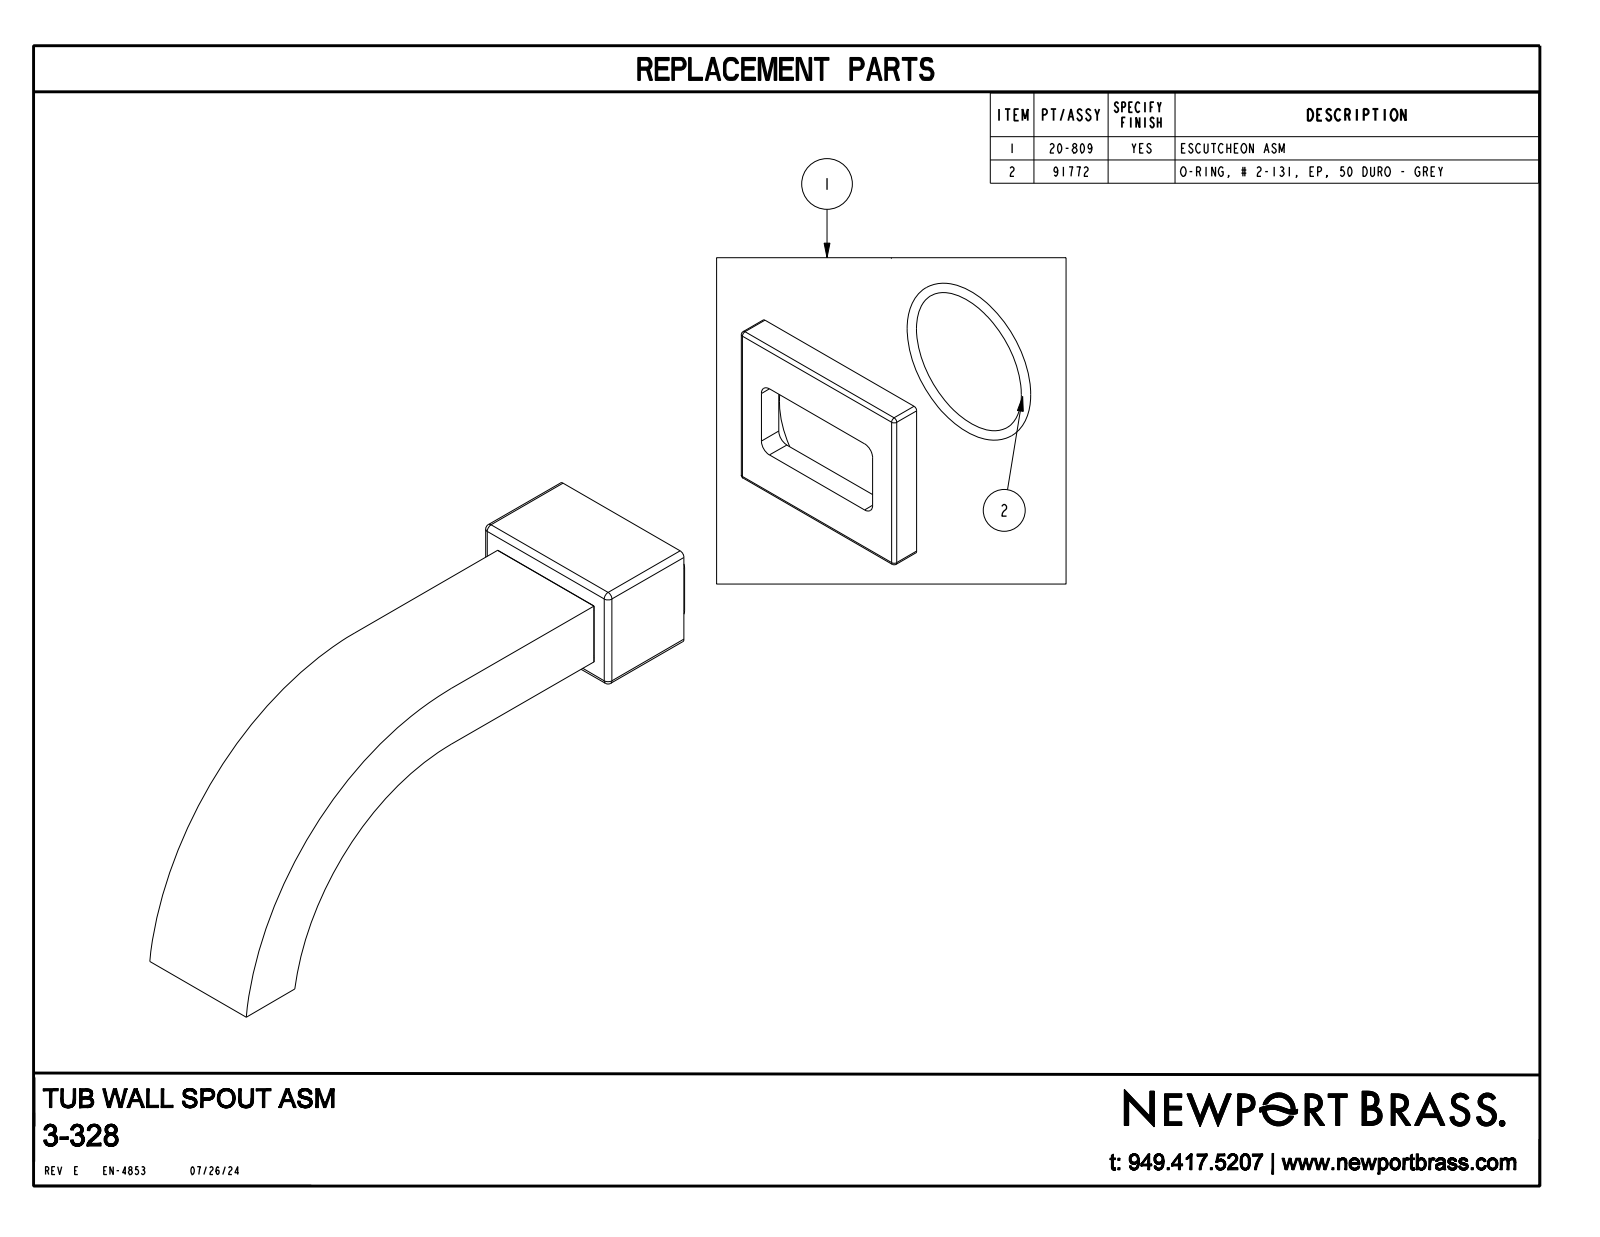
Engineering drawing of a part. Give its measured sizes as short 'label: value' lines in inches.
name: 3-328_SW0001
written by: CREO PARAMETRIC BY PTC INC, 2018400 (AUTOMOTIVE_DESIGN)
unit: in
bodies: 1 solid, 42 faces (16 planar, 18 cylindrical, 8 other)
size: 6.963 × 3.837 × 2.4
volume: 11.96 in³; area: 49.62 in²
rounds: 8× R0.04, 8× R0.06, 1× R2.463, 1× R3.213
face distances: 1.5, 0.235, 0.985, 0.75, 0.22, 1.72, 1.22, 0.35, 0.375, 0.61
